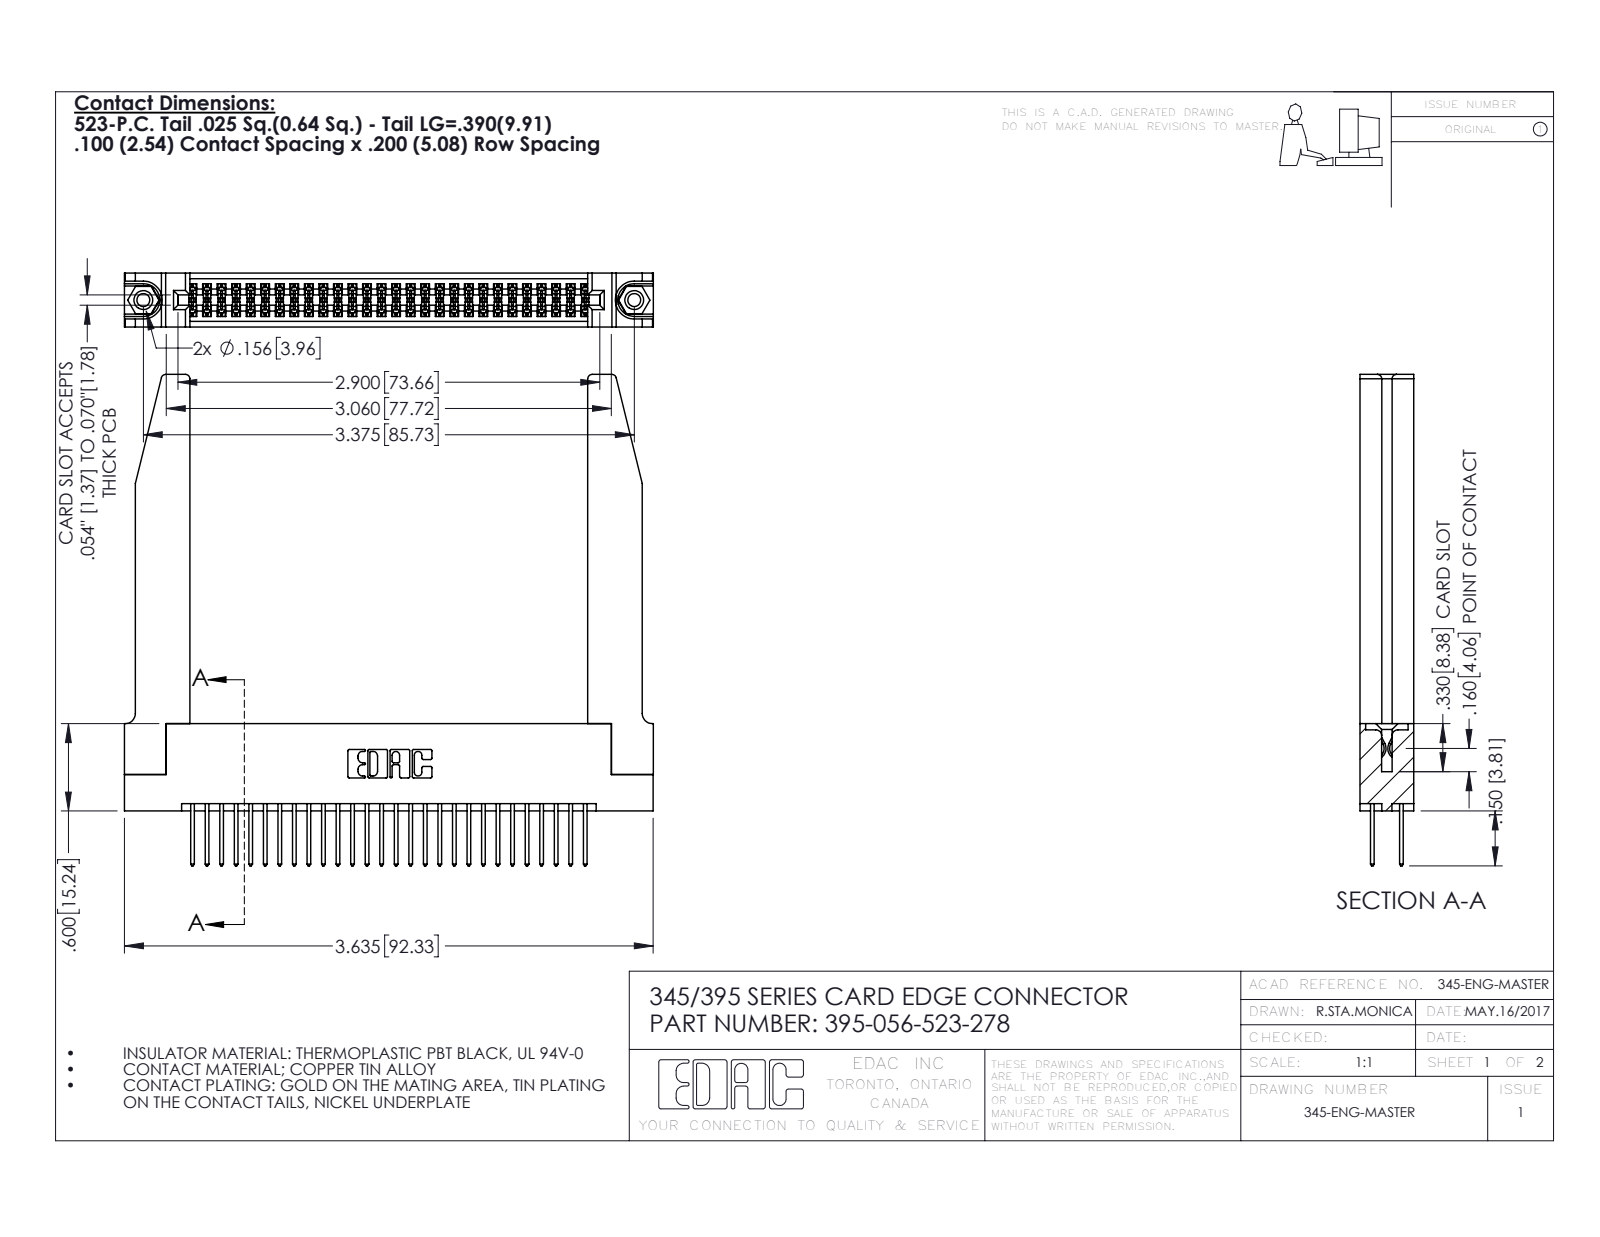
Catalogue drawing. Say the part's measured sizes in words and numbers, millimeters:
The part is named "345 Part_Flush Mounting Lugs - 0.156 Dia-TH; 345-250-001_345-250-001-102; 395-056-523-278; 345-220-078_345-220-078 (+1 more)". Its 3-D file was written by "SolidWorks 2016 (CONFIG_CONTROL_DESIGN)". It is 61 solids with 3160 faces: 2070 planar, 1038 cylindrical and 52 other. Overall it measures 92.4 by 85.8 by 9.4 millimeters. Its volume is 16 730 cubic millimeters and its surface area 20 320 square millimeters. Round holes: 2 of diameter 2.3, 2 of diameter 3.2, 2 of diameter 4, 1 of diameter 1.6. Round bosses or shafts: 2 of diameter 3.9. Partial cylindrical surfaces (rounded edges, fillets, slot ends): 84 of radius 0.2, 56 of radius 0.3, 22 of radius 0.3, 8 of radius 0.8, 6 of radius 0.2, 6 of radius 0.8, 3 of radius 0.7, 2 of radius 0.4. The main face-to-face distances are 9.4, 1.8, 7.6, 5.1, 2.5, 6.9, 0.6, 5.7, 3.8, 3.8. The hole center spacings are 6.9, 79.8, 85.7.
